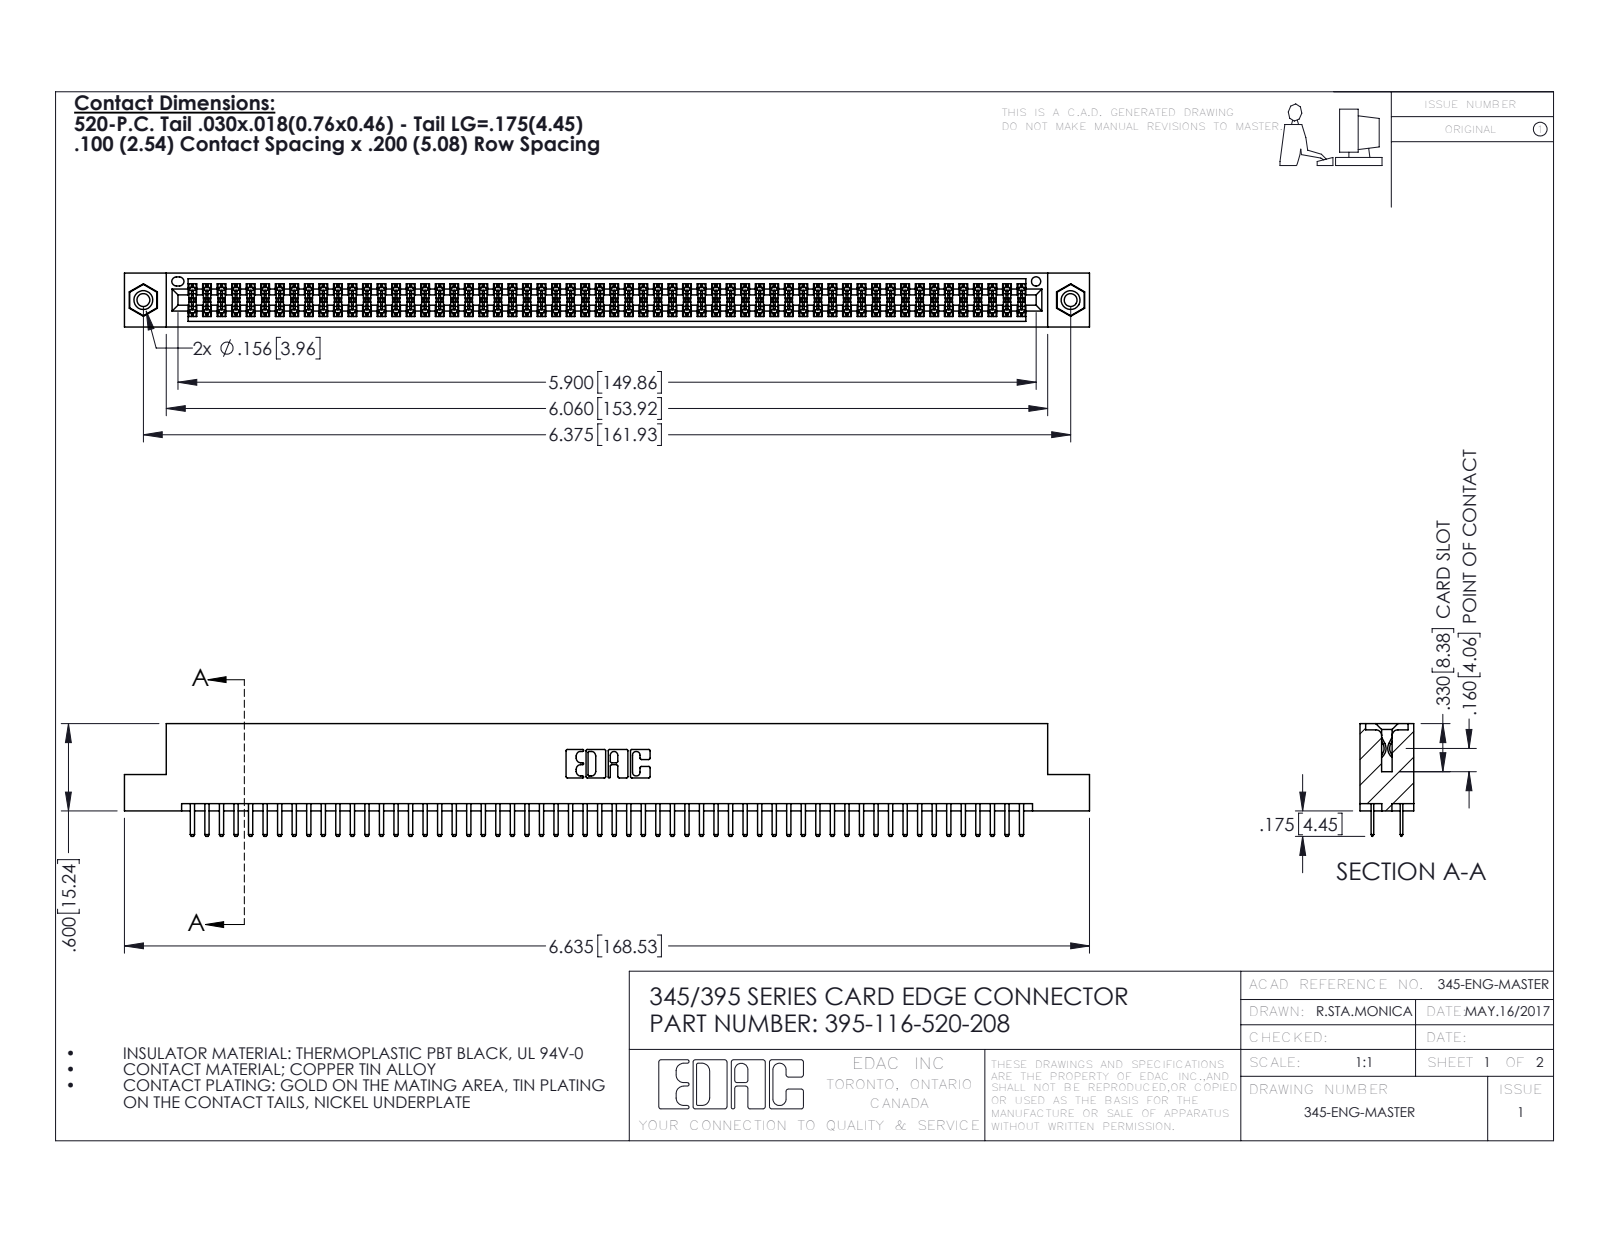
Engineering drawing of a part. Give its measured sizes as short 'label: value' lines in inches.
name: 345-292-001_345-293-120; 395-116-520-208; 345 Part_Flush Mounting Lugs - 0.156 Dia-TI; 345-250-001_345-250-003-102
written by: SolidWorks 2016 (CONFIG_CONTROL_DESIGN)
unit: in
bodies: 119 solids, 6450 faces (4172 planar, 2262 cylindrical, 16 other)
size: 6.635 × 0.775 × 0.37
volume: 1.005 in³; area: 38.05 in²
holes: 2× ⌀0.089, 2× ⌀0.125, 2× ⌀0.156, 1× ⌀0.064
bosses: 2× ⌀0.155
rounds: 174× R0.006, 120× R0.01, 22× R0.01, 6× R0.007, 6× R0.031, 3× R0.026, 2× R0.014, 2× R0.019
face distances: 0.072, 0.298, 0.2, 0.37, 0.098, 0.272, 0.025, 0.225, 0.022, 0.072
hole spacings: 0.27, 6.139, 6.375
